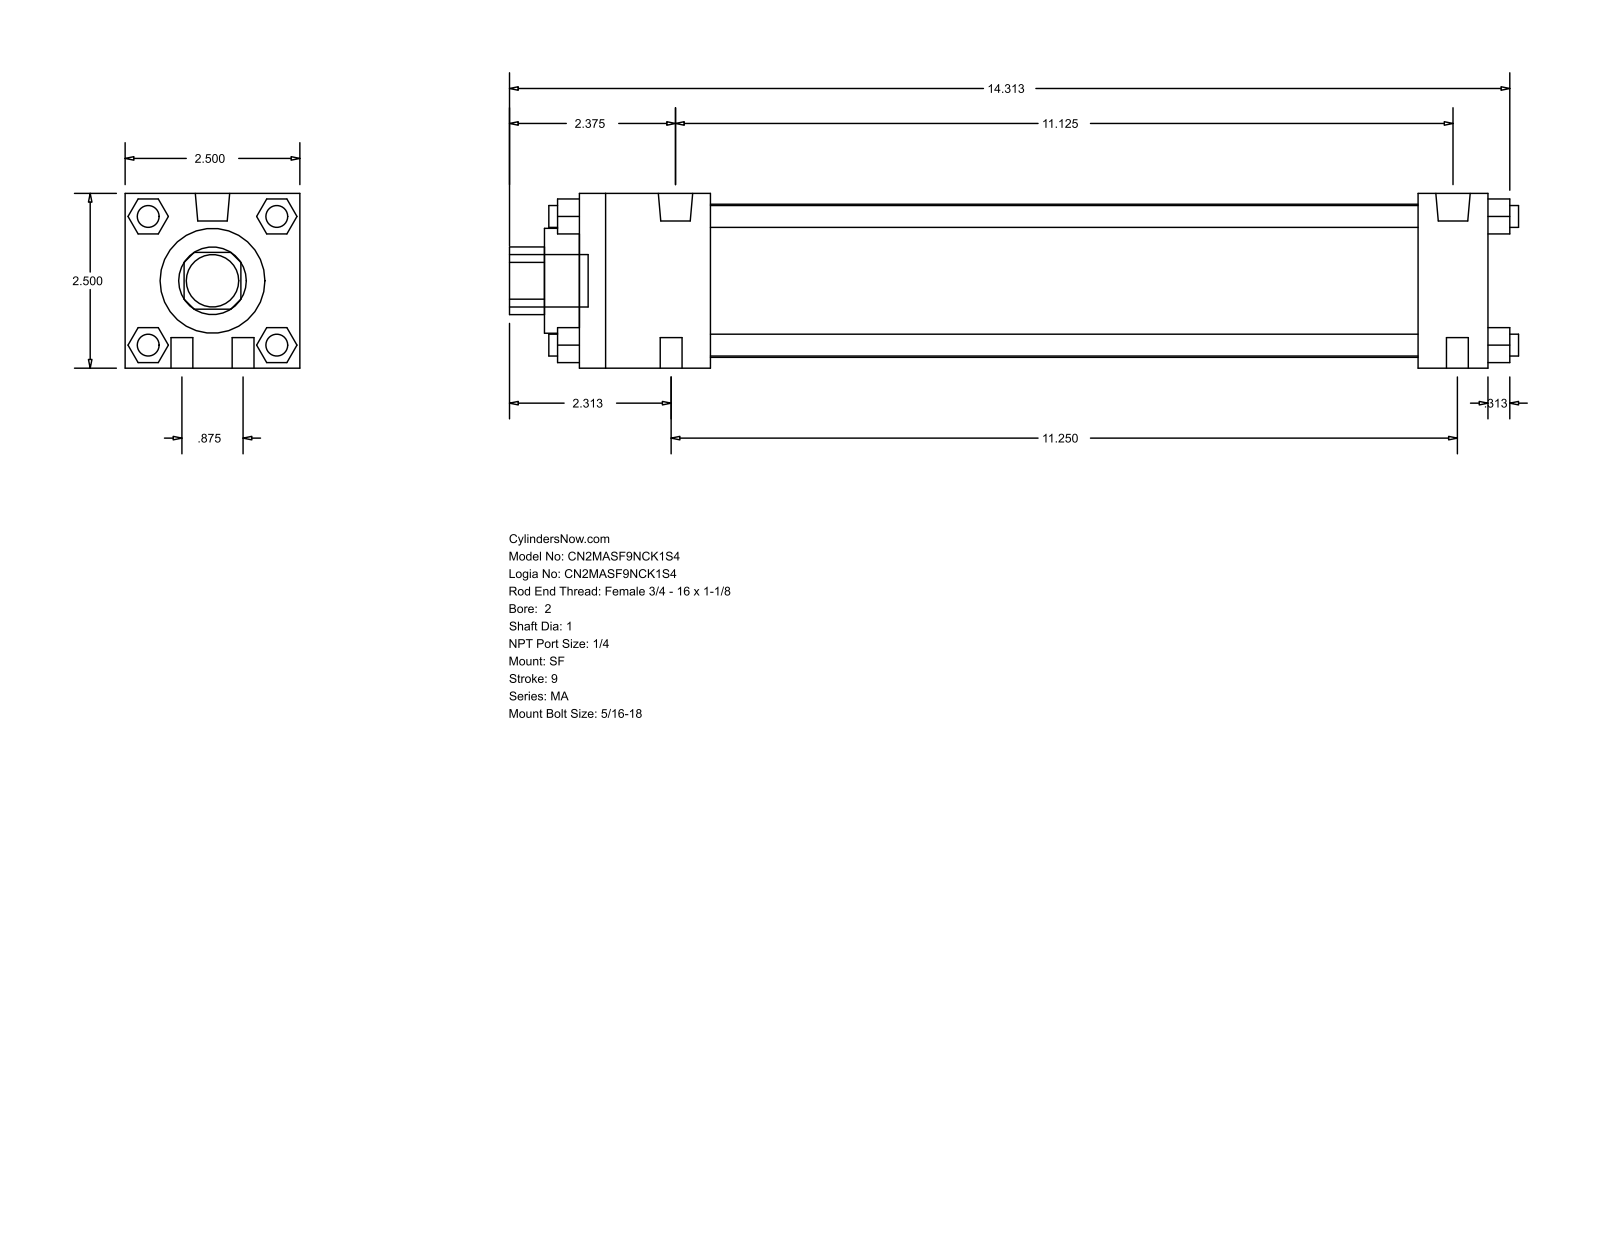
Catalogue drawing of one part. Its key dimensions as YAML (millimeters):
part_name: "MA_SF__0200_1"
step_written_by: "GSSL Pune (CONFIG_CONTROL_DESIGN)"
units: millimeters
bodies: {solids: 0, faces: 124, planar: 94, cylindrical: 30, other: 0}
overall_size: [366.71, 63.5, 63.5]
round_holes:
  - {diameter: 25.4, count: 1}
  - {diameter: 38.1, count: 1}
  - {diameter: 55.63, count: 1}
round_bosses_or_shafts:
  - {diameter: 7.94, count: 10}
  - {diameter: 12.49, count: 2}
  - {diameter: 19.05, count: 1}
partial_cylinders:
  - {radius: 12.29, count: 1}
face_to_face_distances: [63.5, 330.2, 12.7, 25.4, 304.8, 47.63, 257.17, 282.57, 23.37, 40.47]
